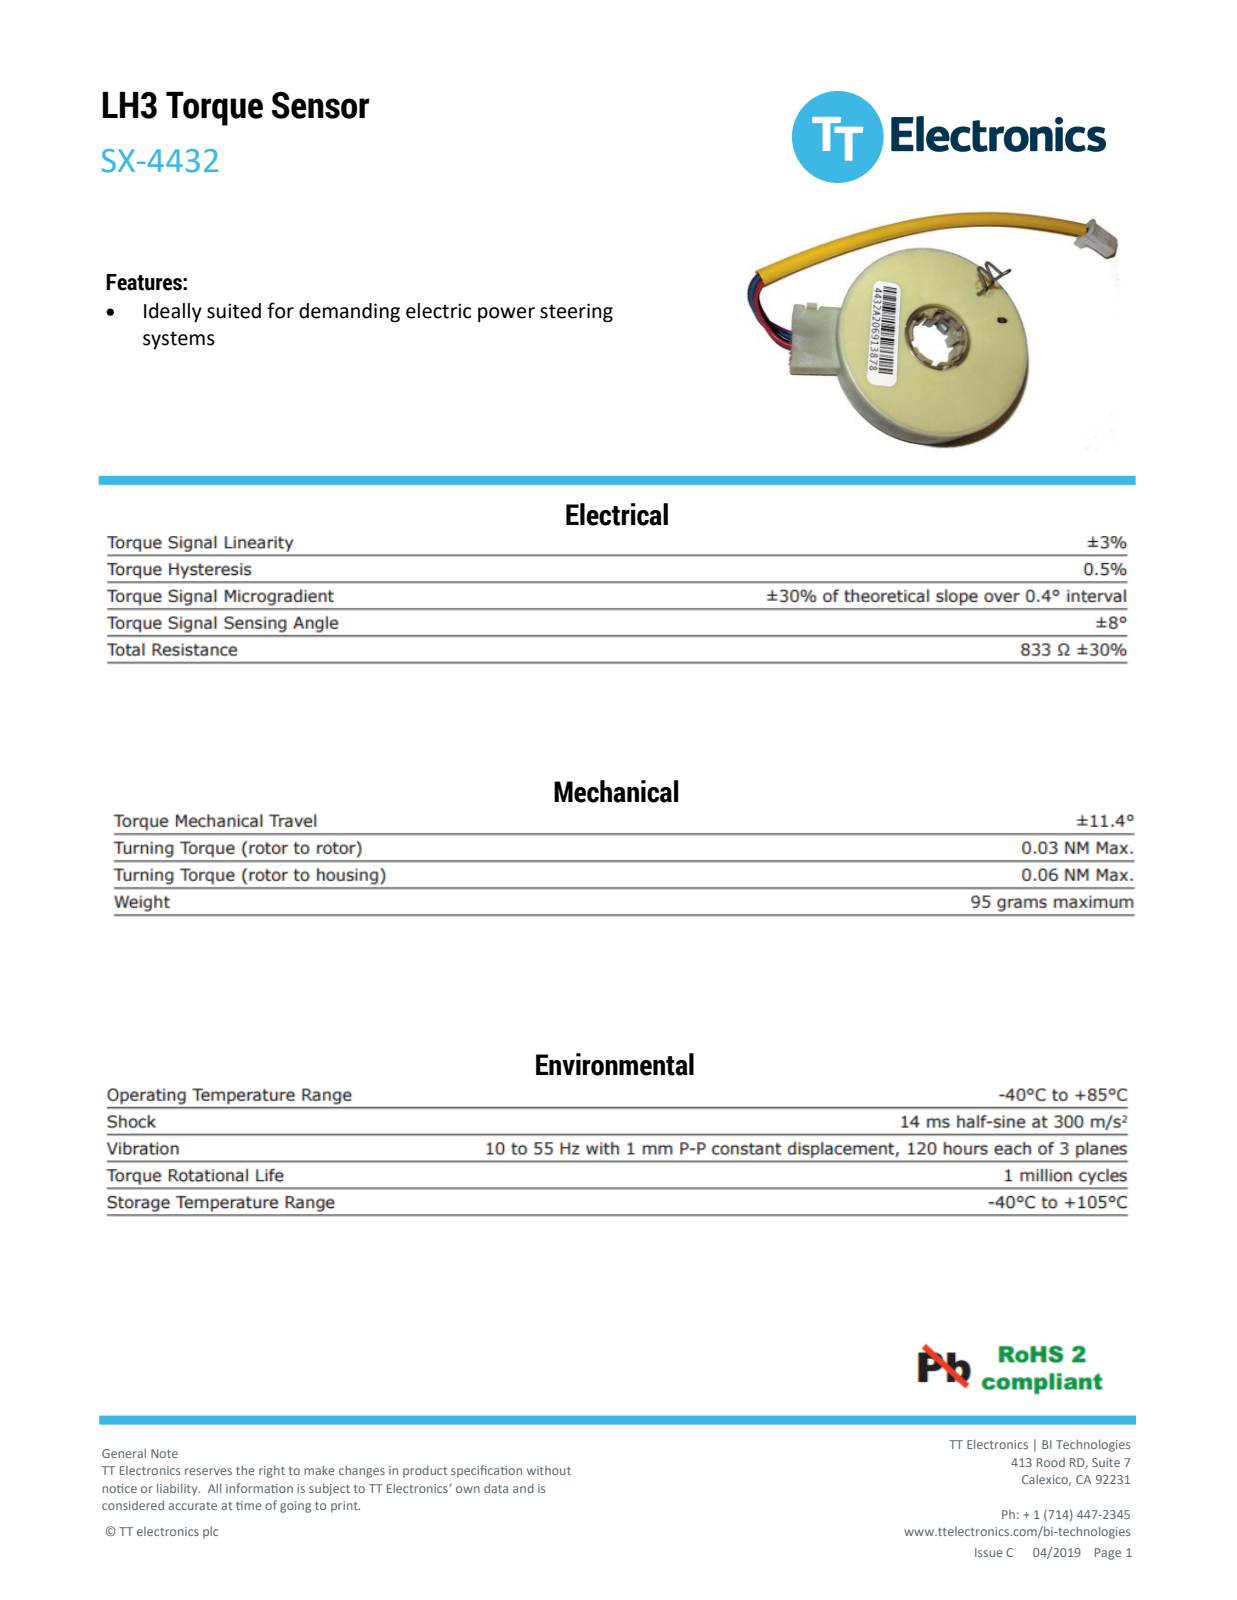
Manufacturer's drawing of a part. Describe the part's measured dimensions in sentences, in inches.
The part is named "SX-4432A_SW0001". Its 3-D file was written by "PRO/ENGINEER BY PARAMETRIC TECHNOLOGY CORPORATION, 2011490 (CONFIG_CONTROL_DESIGN)". It is 4 solids with 1837 faces: 839 planar, 628 cylindrical and 370 other. Overall it measures 8.552 by 3.2 by 1.728 inches. Its volume is 5.39 cubic inches and its surface area 49.38 square inches. Round holes: 4 of diameter 0.042, 2 of diameter 0.039, 1 of diameter 0.049, 1 of diameter 0.29, 1 of diameter 0.985, 1 of diameter 1.046, 1 of diameter 1.126, 1 of diameter 1.146, 1 of diameter 1.2, 1 of diameter 1.255, 1 of diameter 3.15. Round bosses or shafts: 10 of diameter 0.04, 6 of diameter 0.047, 1 of diameter 3.2, 1 of diameter 3.142, 1 of diameter 3.1, 1 of diameter 3.056, 1 of diameter 1.345, 1 of diameter 1.234. Partial cylindrical surfaces (rounded edges, fillets, slot ends): 72 of radius 0.007, 72 of radius 0.012, 63 of radius 0.01, 44 of radius 0.005, 32 of radius 0.01, 21 of radius 0.02, 19 of radius 0.016, 18 of radius 0.006. The main face-to-face distances are 0.719, 0.087, 0.275, 0.444, 0.108, 0.012, 0.065, 0.521, 0.729, 0.161. The hole center spacings are 0.115, 0.345, 0.03, 0.085, 0.23, 0.26, 0.375, 0.46.
